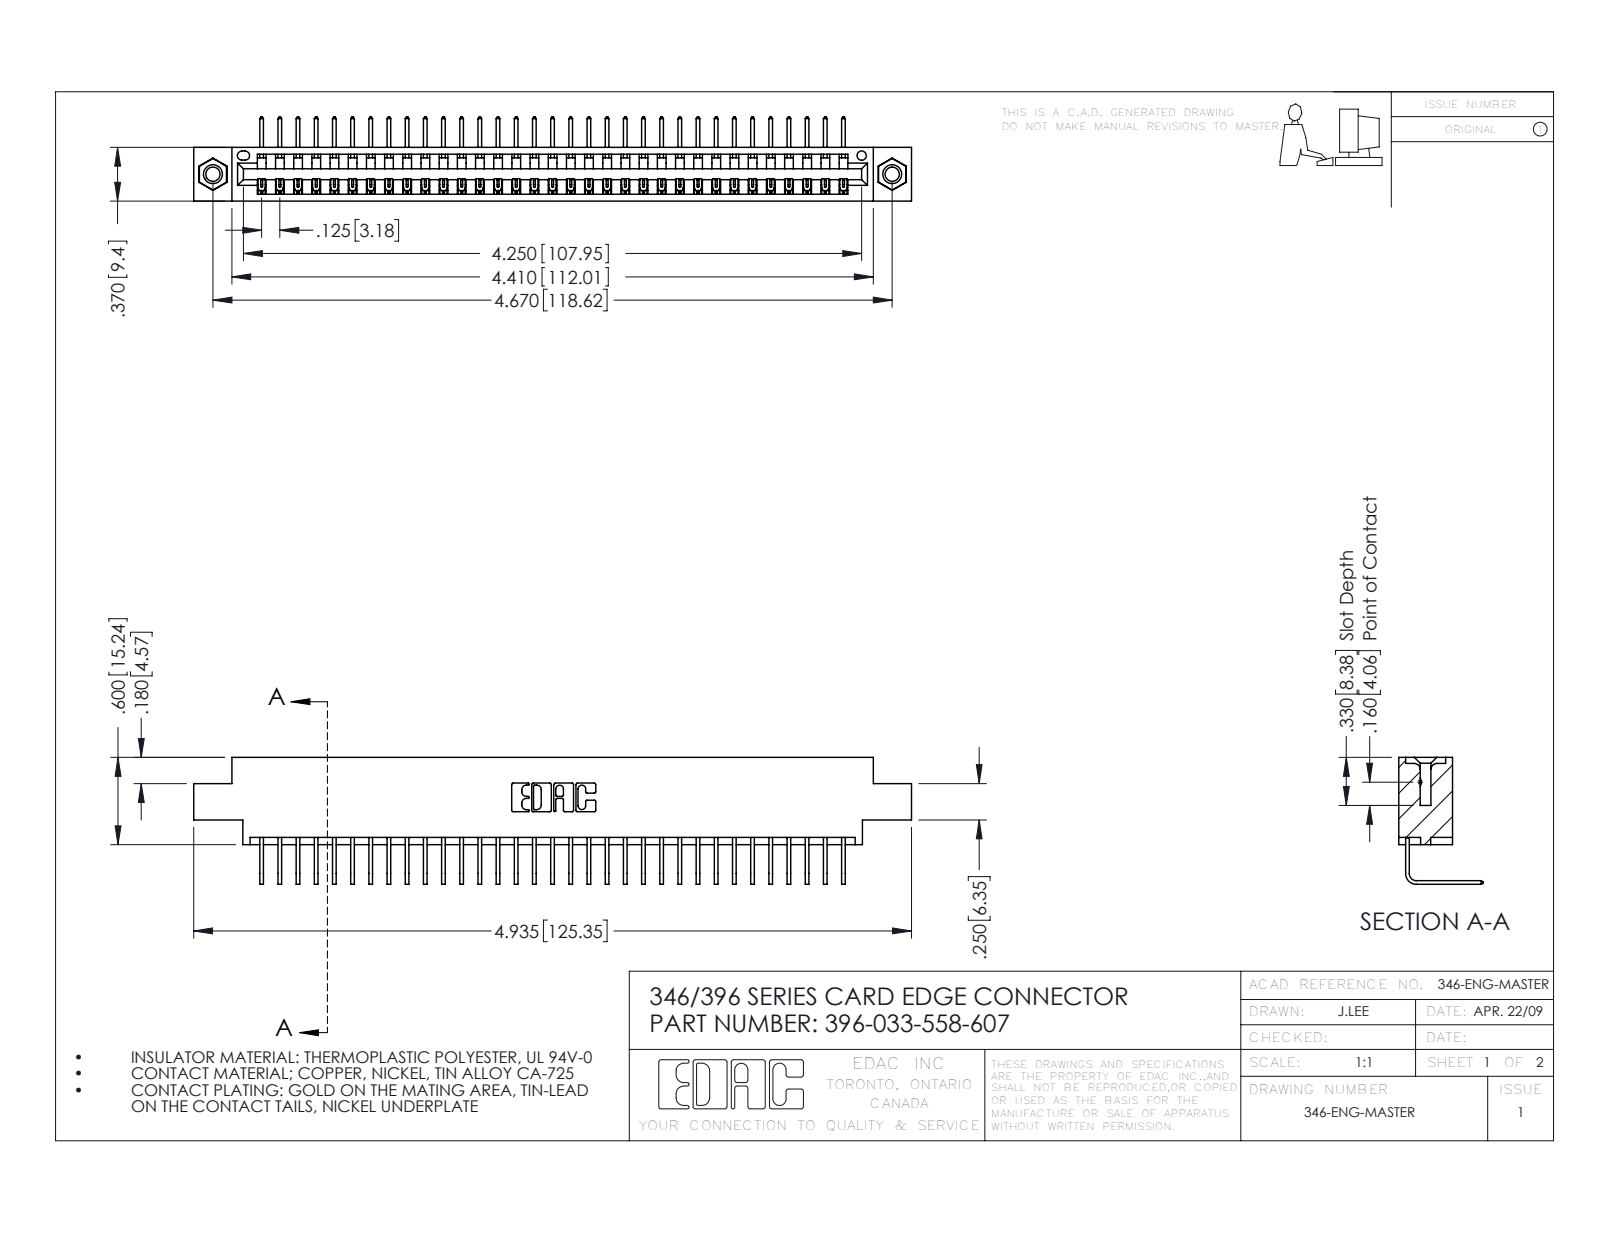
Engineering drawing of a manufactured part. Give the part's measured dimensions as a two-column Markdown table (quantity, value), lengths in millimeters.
| quantity | value |
| --- | --- |
| part name | 345-292-001_558 Tail - 2; 345-250-001_345-250-005-103; 396-033-558-607; 346 Part_0.170 Offset - 0.156 Dia-TI |
| STEP written by | SolidWorks 2016 (CONFIG_CONTROL_DESIGN) |
| units | millimeters |
| bodies | 36 solids, 2166 faces (1498 planar, 652 cylindrical, 16 other) |
| overall size | 125.3 × 22.2 × 14.7 |
| volume | 11 900 mm³ |
| surface area | 15 600 mm² |
| round holes (diameter × count) | 2.5 × 2, 3.2 × 2, 4 × 2, 1.6 × 1 |
| round bosses / shafts (diameter × count) | 3.9 × 2 |
| partial cylindrical surfaces (radius × count) | 0.2 × 66, 0.3 × 22, 0.2 × 6, 0.8 × 6, 0.7 × 3, 0.8 × 2, 1 × 2, 0.4 × 1 |
| main face-to-face distances | 8.2, 1.2, 9.4, 6.4, 7.6, 0.6, 1.8, 5.6, 3.8, 2.5 |
| hole center spacings | 6.2, 113.3, 118.6 |
